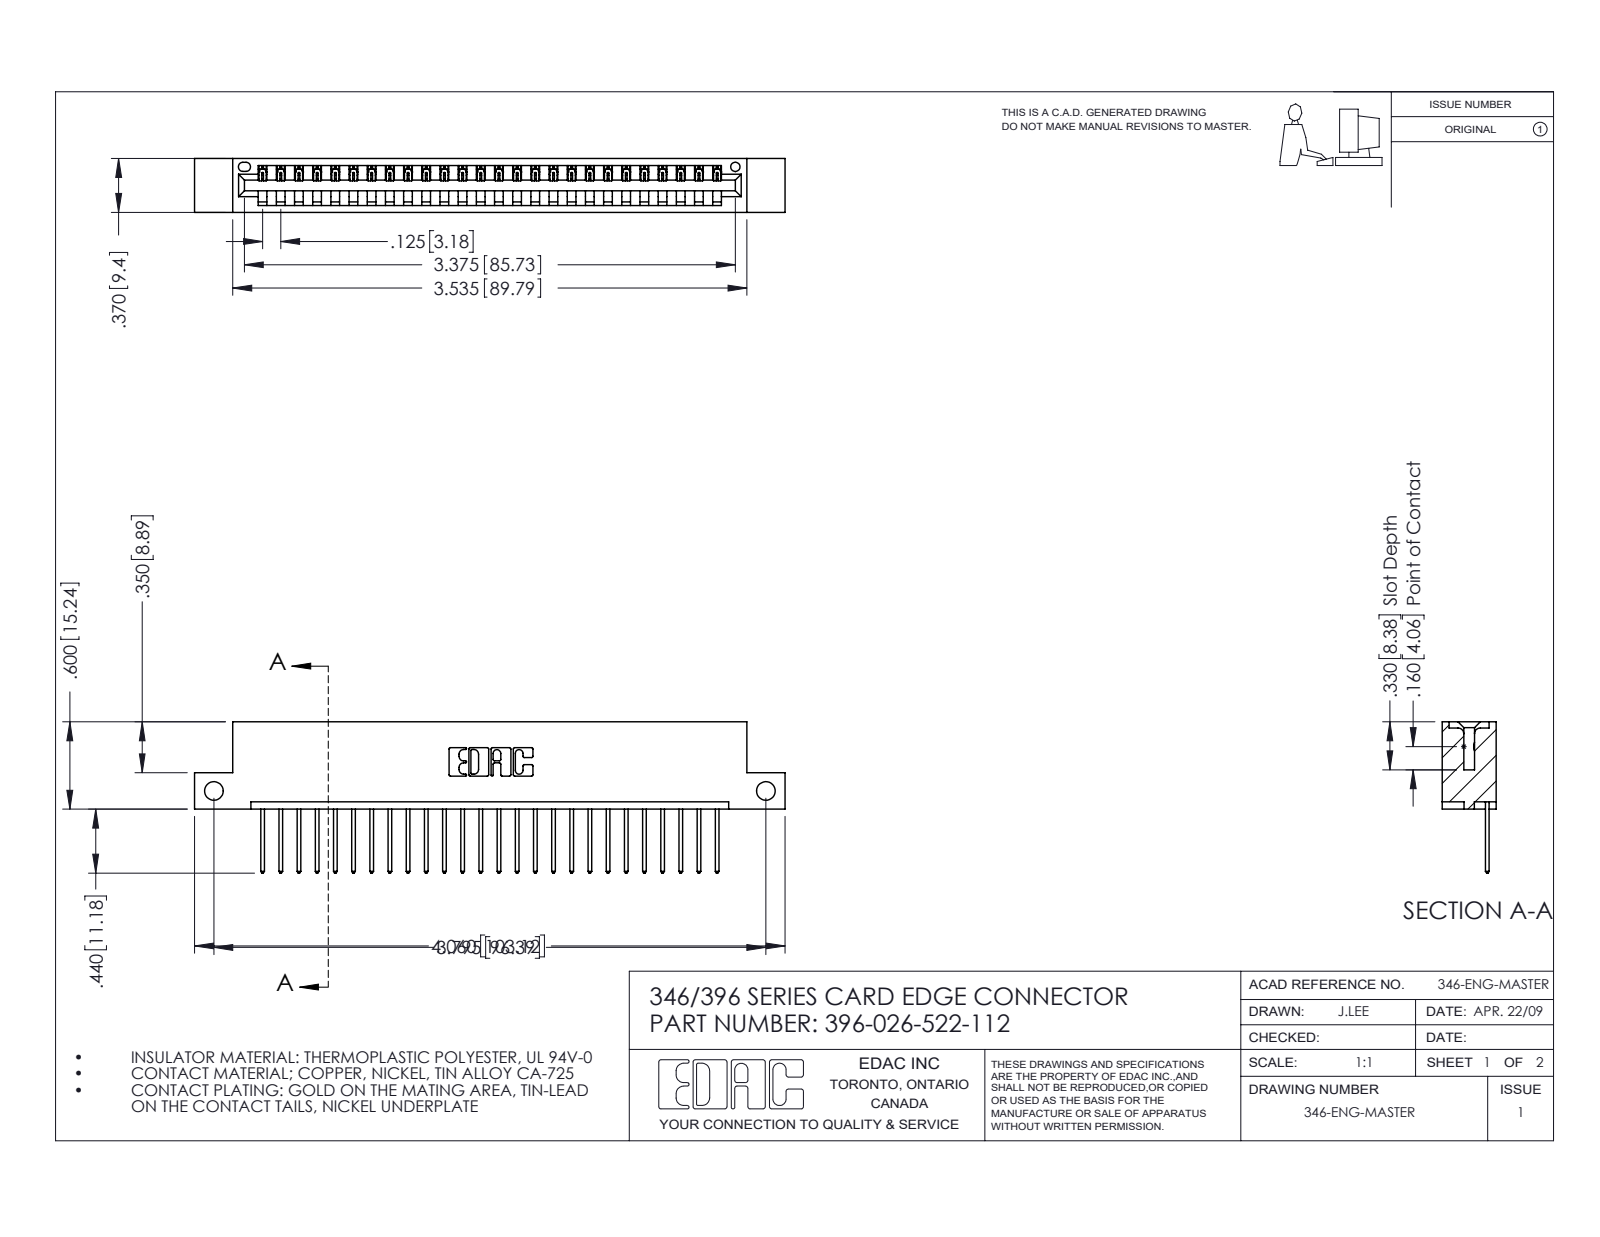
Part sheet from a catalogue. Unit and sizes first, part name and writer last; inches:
Units: inches
Overall size (bounding box): 4.06 × 1.04 × 0.37
Round holes (diameter × count): ⌀0.128 ×2, ⌀0.064 ×1
Partial cylindrical surfaces — rounded edges, fillets, slot ends (radius × count): R0.006 ×52, R0.01 ×52, R0.01 ×22, R0.007 ×6, R0.031 ×6, R0.026 ×3, R0.031 ×2, R0.04 ×2
Main face-to-face distances: 0.048, 0.322, 0.25, 0.37, 0.072, 0.298, 0.025, 0.148, 0.222, 0.1
Hole centre spacings: 3.795
Volume: 0.591 in³ · Surface area: 18.4 in²
Bodies: 27 solids, 1630 faces (1116 planar, 514 cylindrical, 0 other)
Part name (STEP PRODUCT): 396-026-522-112; 345-292-001_345-293-122; 346 Part_Flush Mounting Lugs - Side Mount
STEP written by: SolidWorks 2016 (CONFIG_CONTROL_DESIGN)
